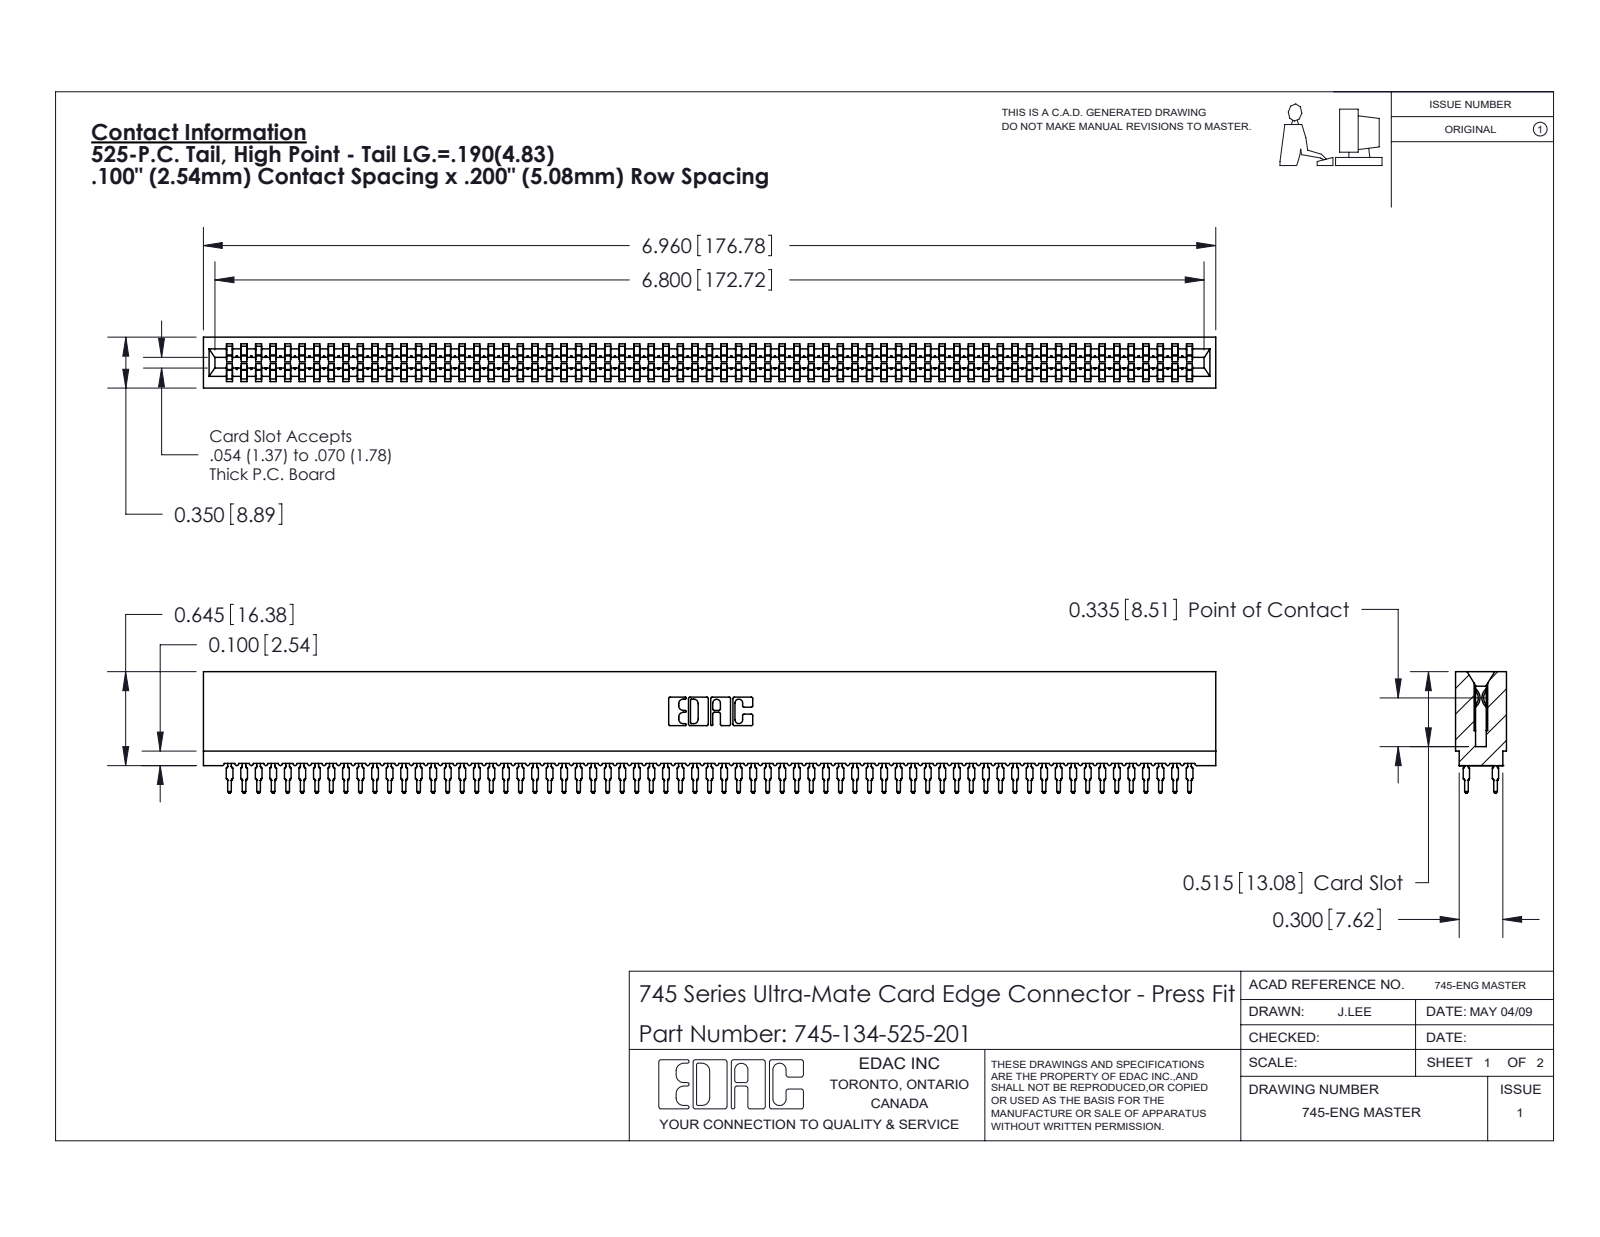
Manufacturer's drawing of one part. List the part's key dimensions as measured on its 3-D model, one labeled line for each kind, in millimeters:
Part name (STEP PRODUCT): 745-292-001_525; 745-134-525-201; 745 Part_Insulator Option - 01
STEP written by: SolidWorks 2020 (CONFIG_CONTROL_DESIGN)
Units: millimetres
Bodies: 135 solids, 12088 faces (6219 planar, 2385 cylindrical, 3484 other)
Overall size (bounding box): 176.8 × 21.2 × 8.9
Volume: 15 700 mm³ · Surface area: 32 440 mm²
Partial cylindrical surfaces — rounded edges, fillets, slot ends (radius × count): R0.5 ×268, R0.4 ×134, R0.3 ×22, R0.1 ×8, R0.3 ×8, R0.2 ×6, R0.8 ×6, R0.7 ×3
Main face-to-face distances: 8.9, 1.6, 7.3, 1.1, 7.7, 0.5, 6.2, 3.5, 5.4, 2.4
